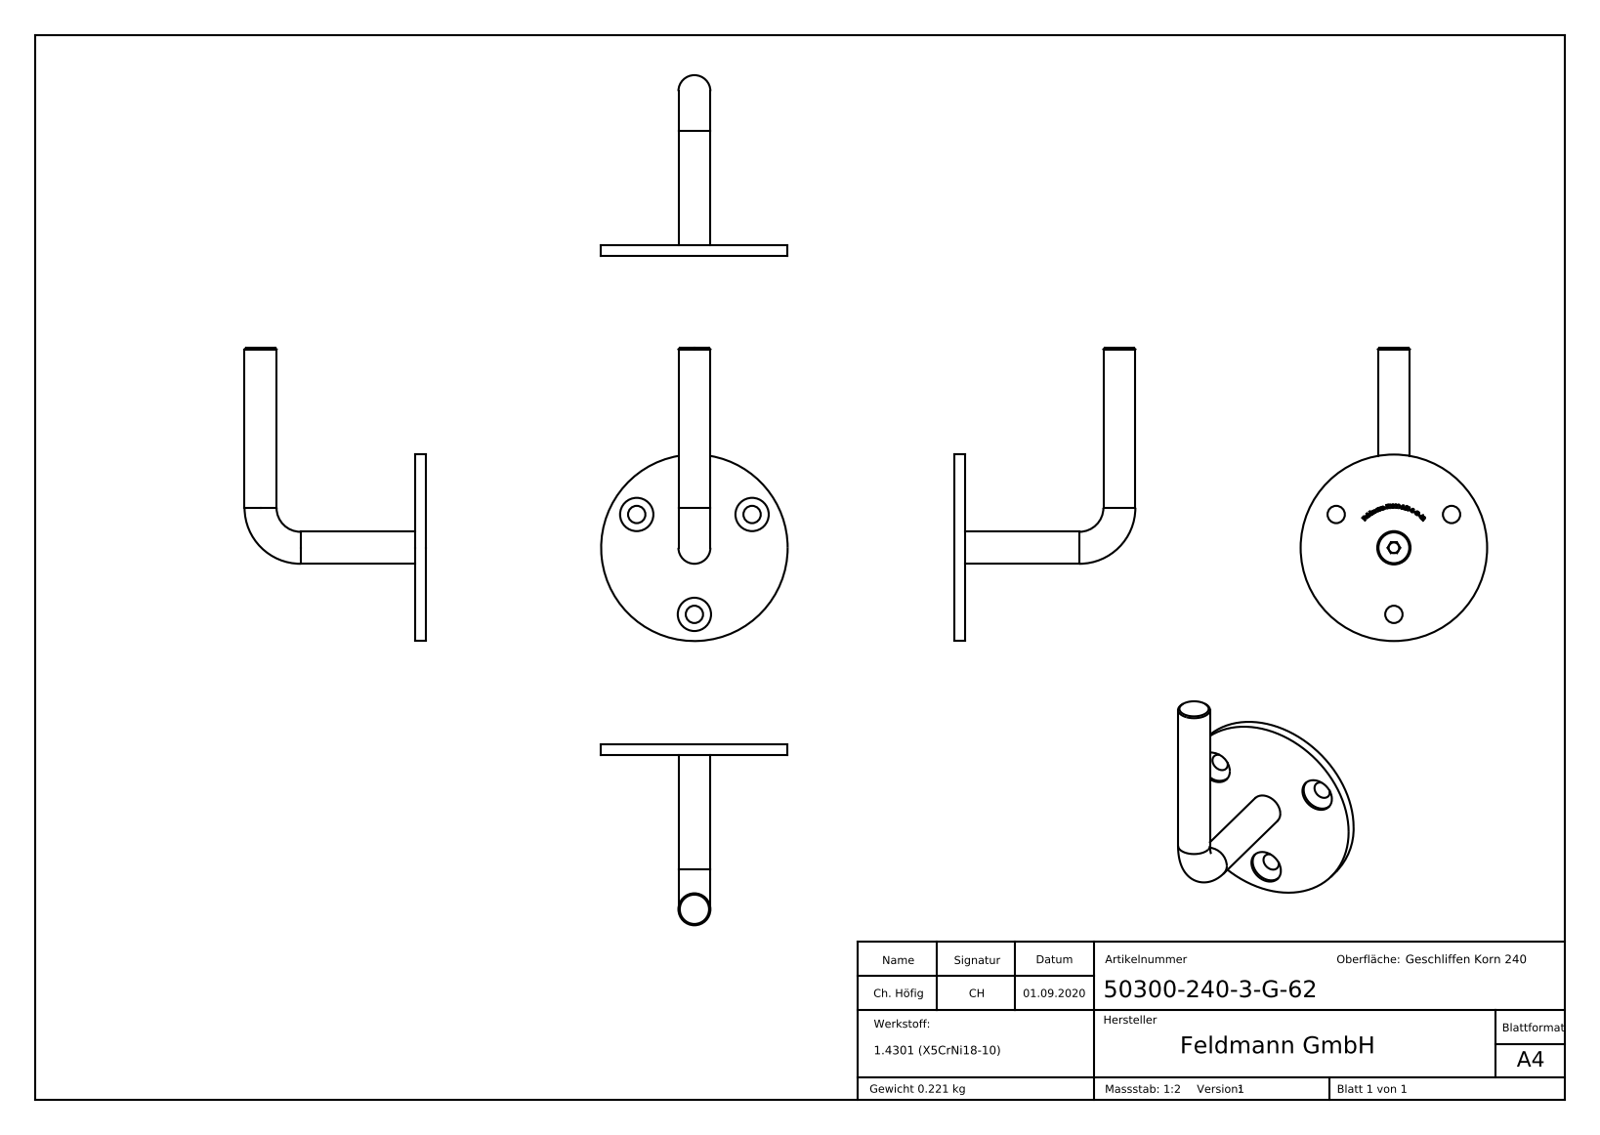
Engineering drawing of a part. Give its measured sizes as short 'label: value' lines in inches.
name: 50300-240-62 Teil2; 50300-240-3-G-62; socket countersunk head screw_din; 50300-240-62 Teil1_50300-240-3-G-62 Teil1 (+3 more)
written by: SolidWorks 2018 (CONFIG_CONTROL_DESIGN)
unit: in
bodies: 3 solids, 431 faces (165 planar, 44 cylindrical, 222 other)
size: 4.331 × 2.756 × 2.677
volume: 1.731 in³; area: 22.55 in²
holes: 4× ⌀0.492, 1× ⌀0.197, 1× ⌀0.26
bosses: 2× ⌀0.472, 1× ⌀2.756, 1× ⌀0.456, 1× ⌀0.236
face distances: 0.157, 0.037, 0.12, 0.667, 0.63, 0.51, 0.158, 0.033, 0.154, 0.663
hole spacings: 0.984, 1.705
